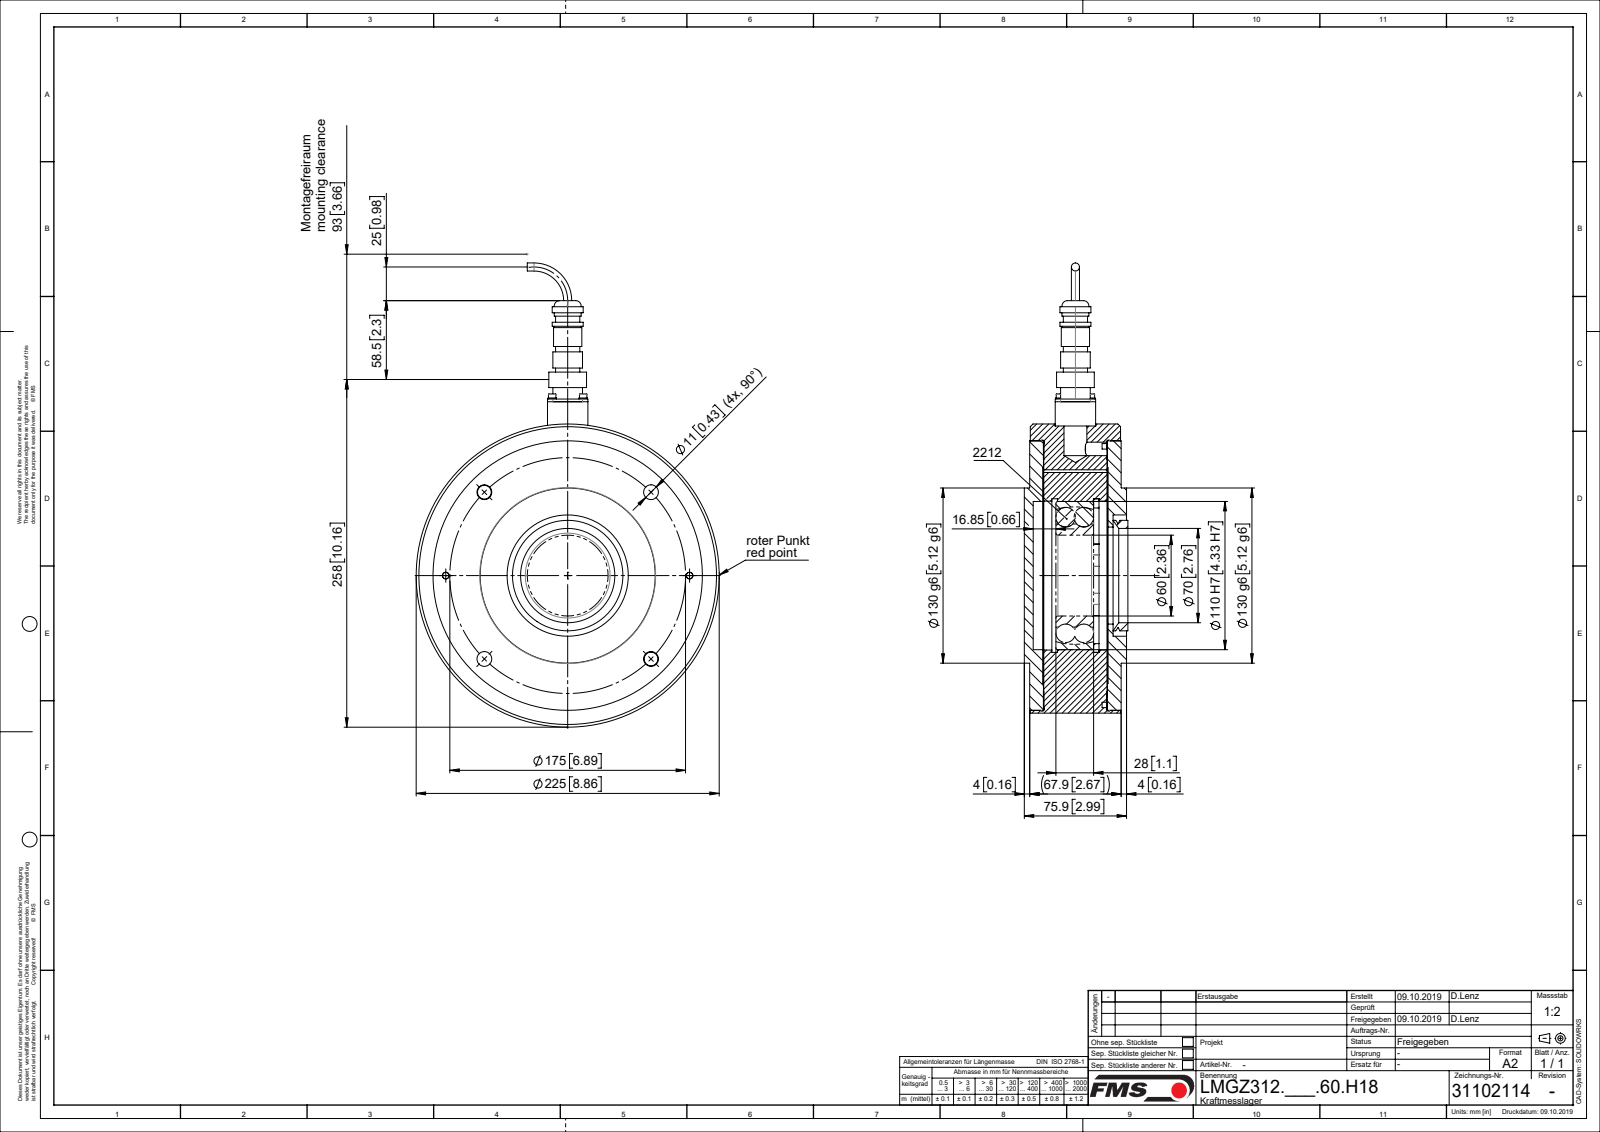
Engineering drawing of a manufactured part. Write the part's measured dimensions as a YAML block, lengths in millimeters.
part_name: "ZEICHNUNG2; L50036; L4765504; TEIL1 (+8 more)"
step_written_by: "Mechanical Desktop 2009 (CONFIG_CONTROL_DESIGN)"
units: millimeters
bodies: {solids: 20, faces: 389, planar: 99, cylindrical: 232, other: 58}
overall_size: [344.5, 225, 75.9]
volume: 2385000
surface_area: 392883
round_holes:
  - {diameter: 11, count: 6}
  - {diameter: 2.6, count: 4}
  - {diameter: 3.2, count: 4}
  - {diameter: 3.4, count: 4}
  - {diameter: 9, count: 4}
  - {diameter: 5, count: 2}
  - {diameter: 6.6, count: 2}
  - {diameter: 60, count: 1}
  - {diameter: 70, count: 1}
  - {diameter: 72, count: 1}
  - {diameter: 88.2, count: 1}
  - {diameter: 90, count: 1}
round_bosses_or_shafts:
  - {diameter: 6.2, count: 4}
  - {diameter: 5.5, count: 4}
  - {diameter: 3, count: 4}
  - {diameter: 2.5, count: 4}
  - {diameter: 6, count: 3}
  - {diameter: 10, count: 2}
  - {diameter: 225, count: 1}
  - {diameter: 199, count: 1}
partial_cylinders:
  - {radius: 4, count: 4}
  - {radius: 81, count: 1}
  - {radius: 86, count: 1}
face_to_face_distances: [47.25, 10.45, 57.7, 10.2, 57.45, 47.5, 9.75, 9.7, 58.2, 0.5]
hole_center_spacings: [23, 68.17, 87.5, 123.74, 164.45, 32.53, 90.5, 174.99]
